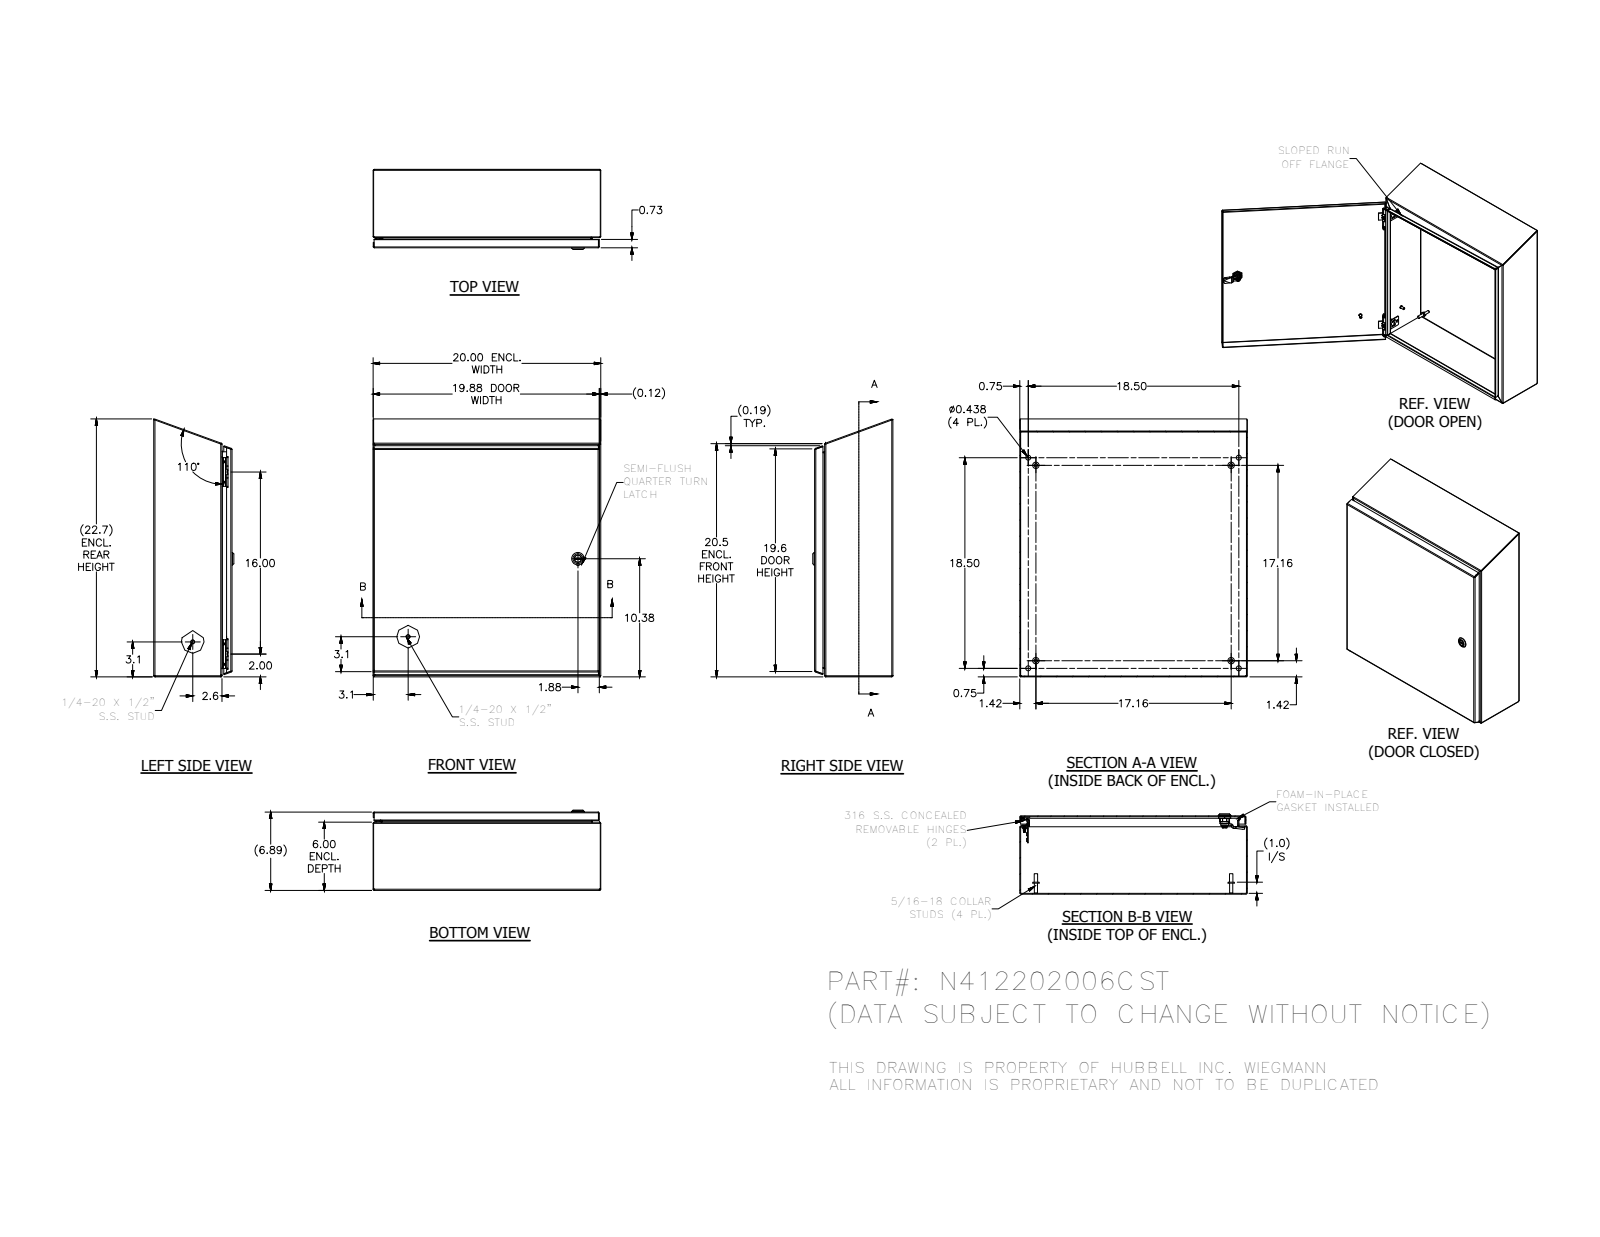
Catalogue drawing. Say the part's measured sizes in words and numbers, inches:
The part is named "N412202006CST". Its 3-D file was written by "SolidWorks 2018 (AUTOMOTIVE_DESIGN)". It is 36 solids with 1521 faces: 568 planar, 552 cylindrical and 401 other. Overall it measures 22.663 by 20 by 7.044 inches. Its volume is 113.5 cubic inches and its surface area 3 086 square inches. Round holes: 4 of diameter 0.093, 4 of diameter 0.152, 4 of diameter 0.167, 4 of diameter 0.172, 4 of diameter 0.187, 4 of diameter 0.437, 3 of diameter 0.156, 1 of diameter 0.187, 1 of diameter 0.197, 1 of diameter 0.315, 1 of diameter 0.394, 1 of diameter 0.402. Round bosses or shafts: 10 of diameter 0.25, 4 of diameter 0.563, 4 of diameter 0.36, 4 of diameter 0.32, 4 of diameter 0.3, 4 of diameter 0.275, 4 of diameter 0.256, 4 of diameter 0.164. Partial cylindrical surfaces (rounded edges, fillets, slot ends): 30 of radius 0.012, 29 of radius 0.031, 26 of radius 0.05, 19 of radius 0.105, 18 of radius 0.016, 16 of radius 0.125, 13 of radius 0.02, 8 of radius 0.032. The main face-to-face distances are 0.074, 6.813, 6.739, 6.887, 19.926, 19.852, 20, 0.074, 5.926, 0.887. The hole center spacings are 16, 18.5, 18.872, 0.5, 0.656, 0.66, 1.307, 1.311.
